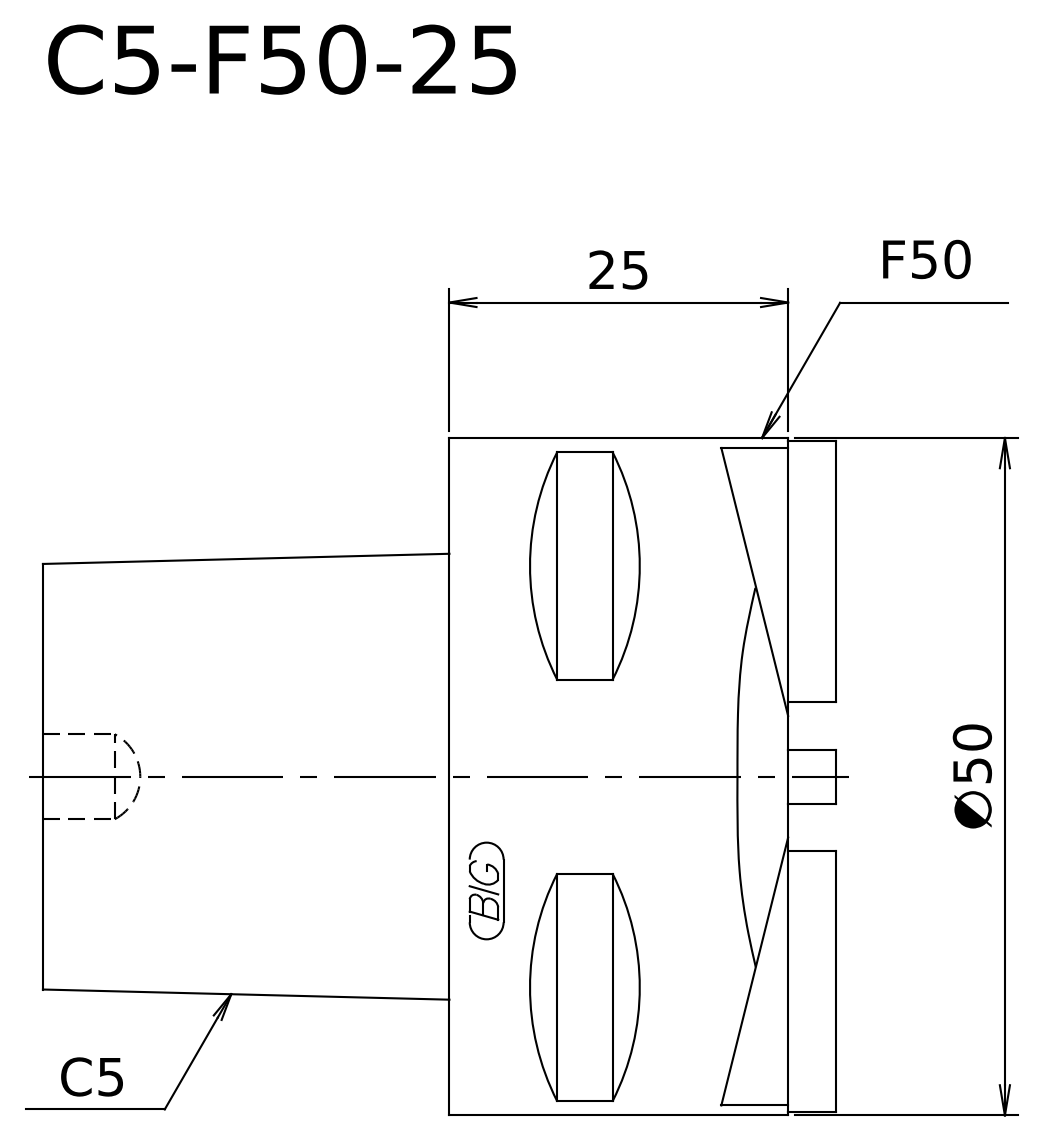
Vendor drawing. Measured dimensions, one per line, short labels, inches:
name: C5-F50-25
written by: SolidWorks 2021 (CONFIG_CONTROL_DESIGN)
unit: in
bodies: 1 solid, 7 faces (3 planar, 2 cylindrical, 2 other)
size: 2.165 × 1.969 × 1.969
volume: 4.483 in³; area: 16.76 in²
bosses: 1× ⌀1.969
face distances: 0.984, 1.181, 2.165
